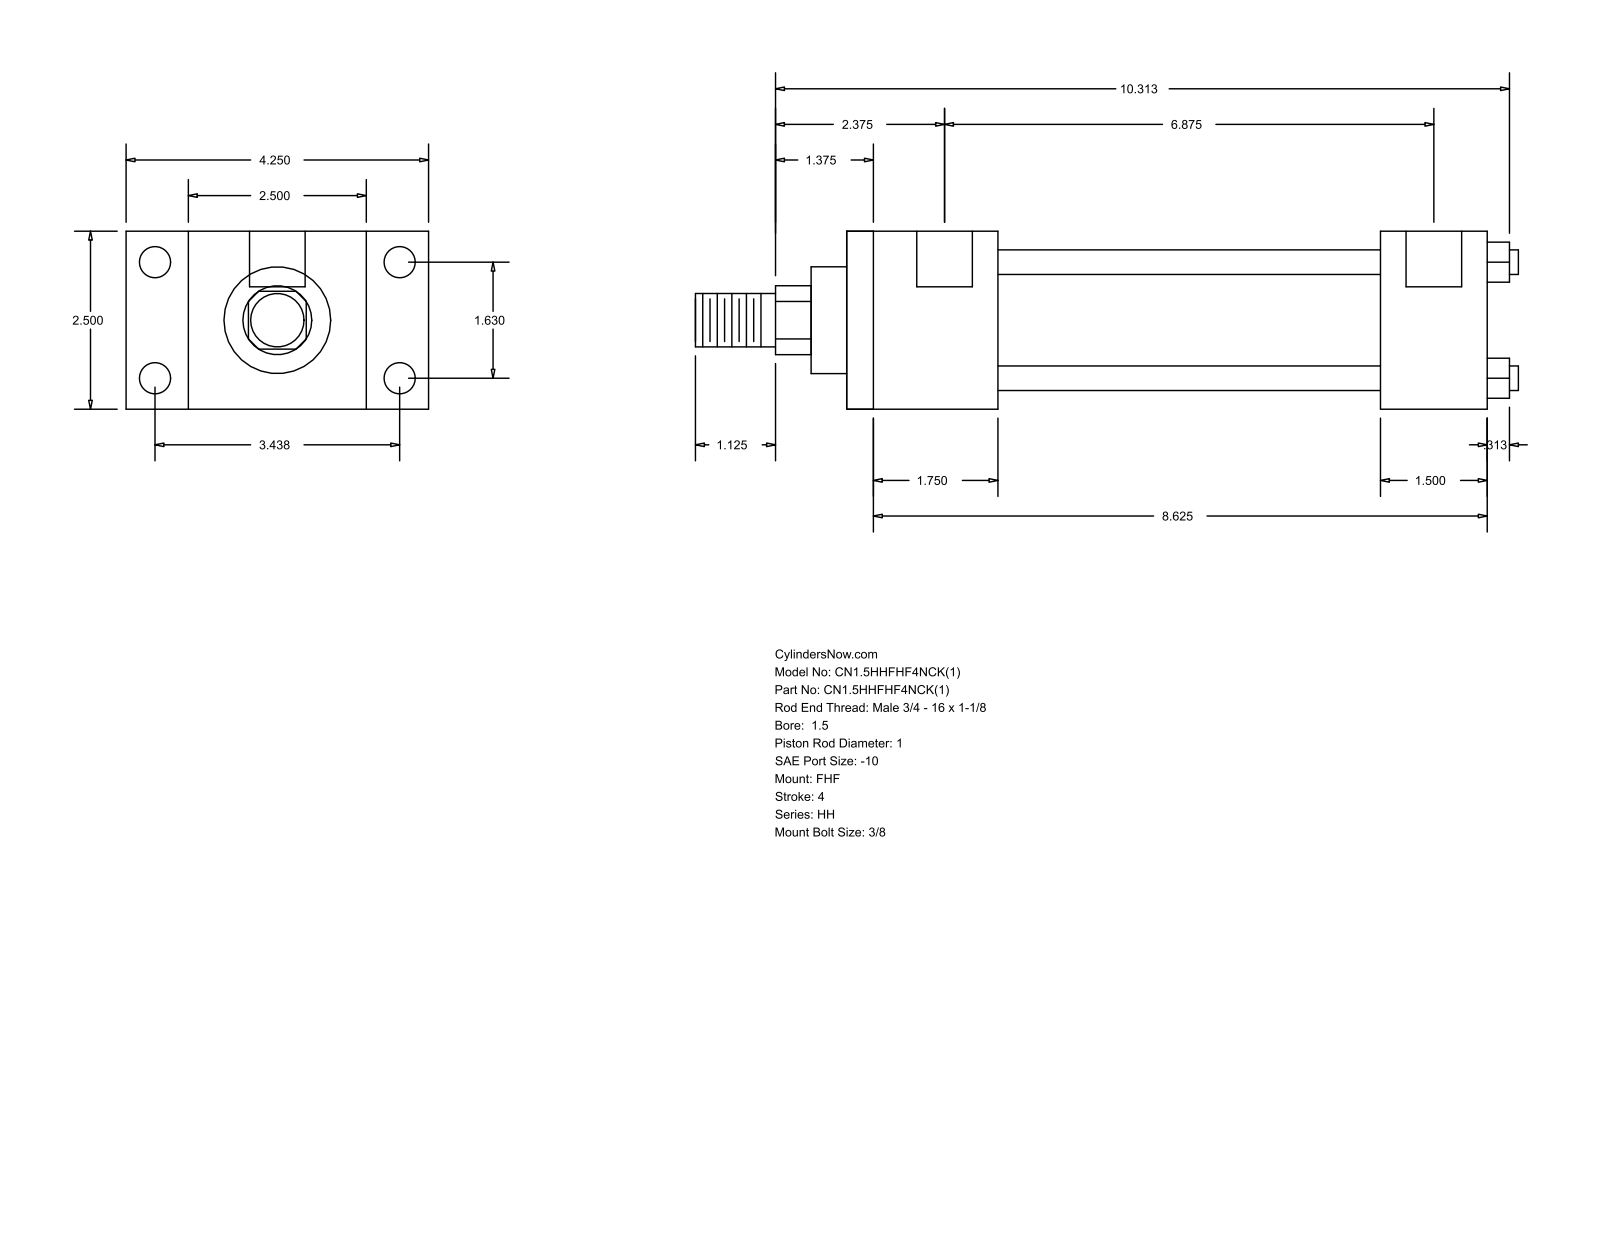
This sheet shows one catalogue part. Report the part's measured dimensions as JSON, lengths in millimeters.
{"part_name": "HH_FHF__0150_1", "step_written_by": "GSSL Pune (CONFIG_CONTROL_DESIGN)", "units": "millimeters", "bodies": {"solids": 0, "faces": 88, "planar": 60, "cylindrical": 28, "other": 0}, "overall_size": [293.69, 107.95, 63.5], "round_holes": [[5.56, 4], [11.13, 4], [19.84, 2]], "round_bosses_or_shafts": [[8.76, 4], [44.45, 1], [38.1, 1], [25.4, 1], [19.05, 1]], "partial_cylinders_radius": [[12.29, 1]], "face_to_face_distances": [63.5, 22.23, 85.73, 53.98, 107.96, 228.6, 174.62, 38.1, 190.5, 136.52], "hole_center_spacings": [1.59, 41.4, 87.32, 96.64, 176.21, 177.8, 174.62]}
